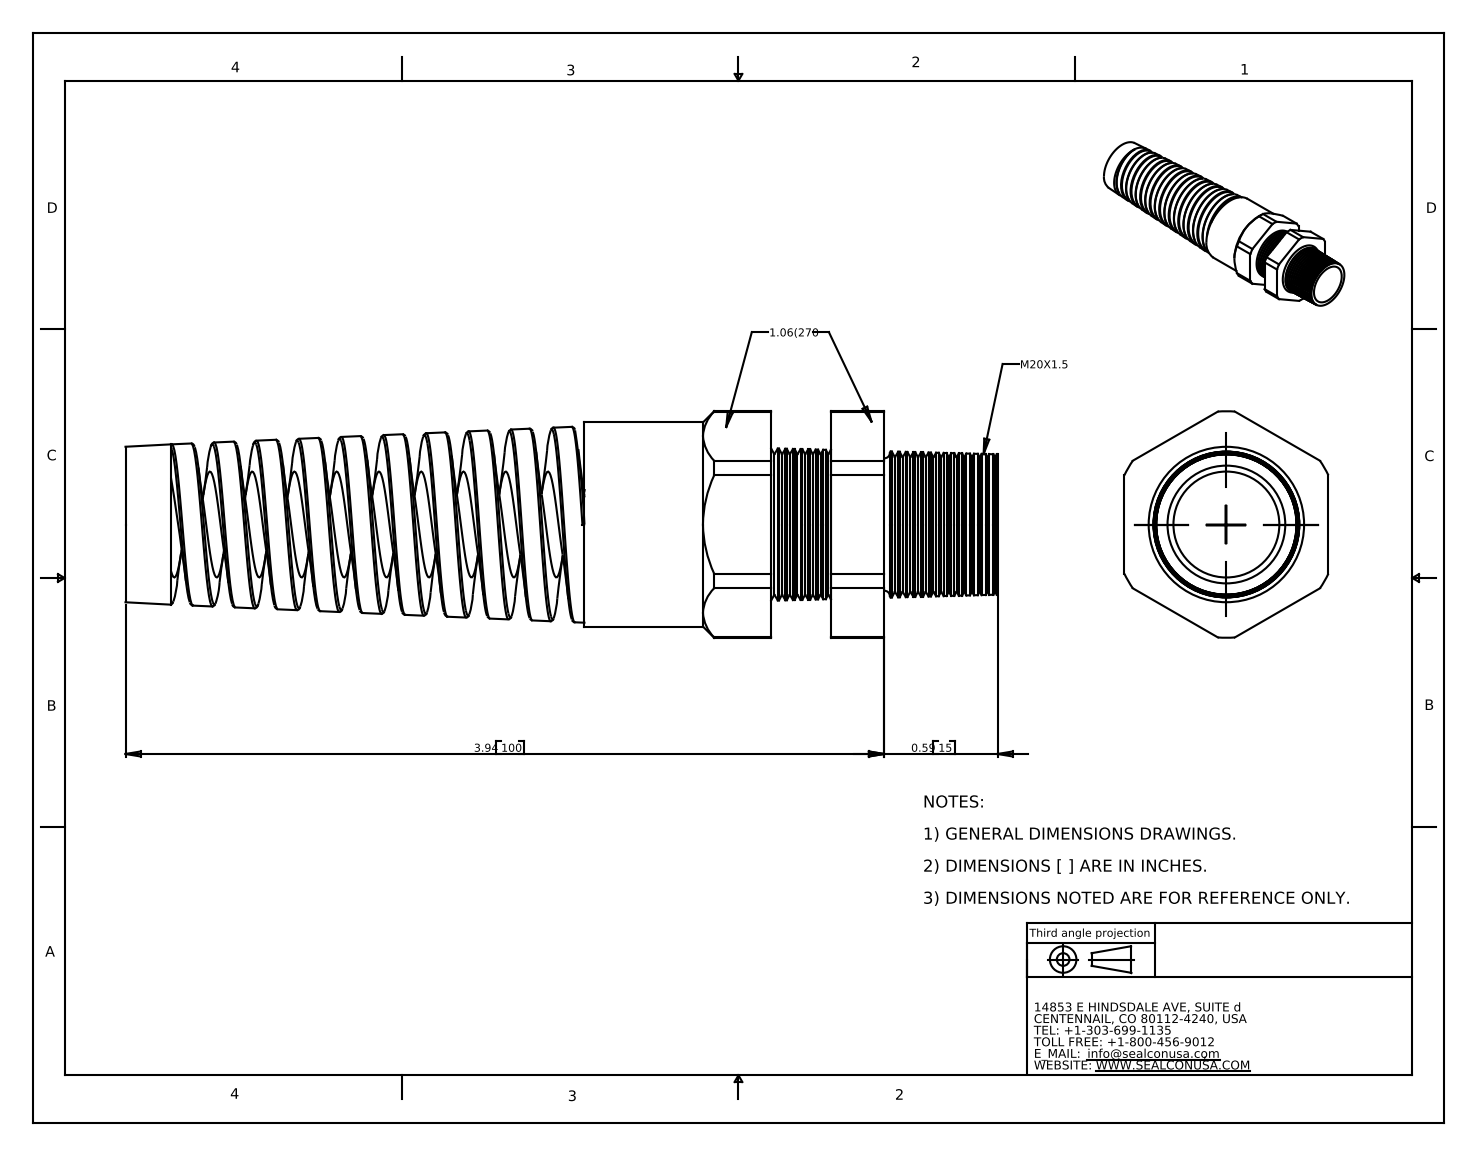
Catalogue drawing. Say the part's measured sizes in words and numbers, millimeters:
The part is named "CF22DA-BK". Its 3-D file was written by "SolidWorks 2007 (CONFIG_CONTROL_DESIGN)". It is 2 solids with 254 faces: 26 planar, 45 cylindrical and 183 other. Overall it measures 115.1 by 29.9 by 26.9 millimeters. Its volume is 26 910 cubic millimeters and its surface area 19 700 square millimeters. Round holes: 1 of diameter 14, 1 of diameter 14.6. Round bosses or shafts: 1 of diameter 26.9, 1 of diameter 19.7. Partial cylindrical surfaces (rounded edges, fillets, slot ends): 1 of radius 14.9. The main face-to-face distances are 26.9, 7.9, 14.9, 7, 24.6, 32.5, 39.5, 15.6, 9, 16.9.
